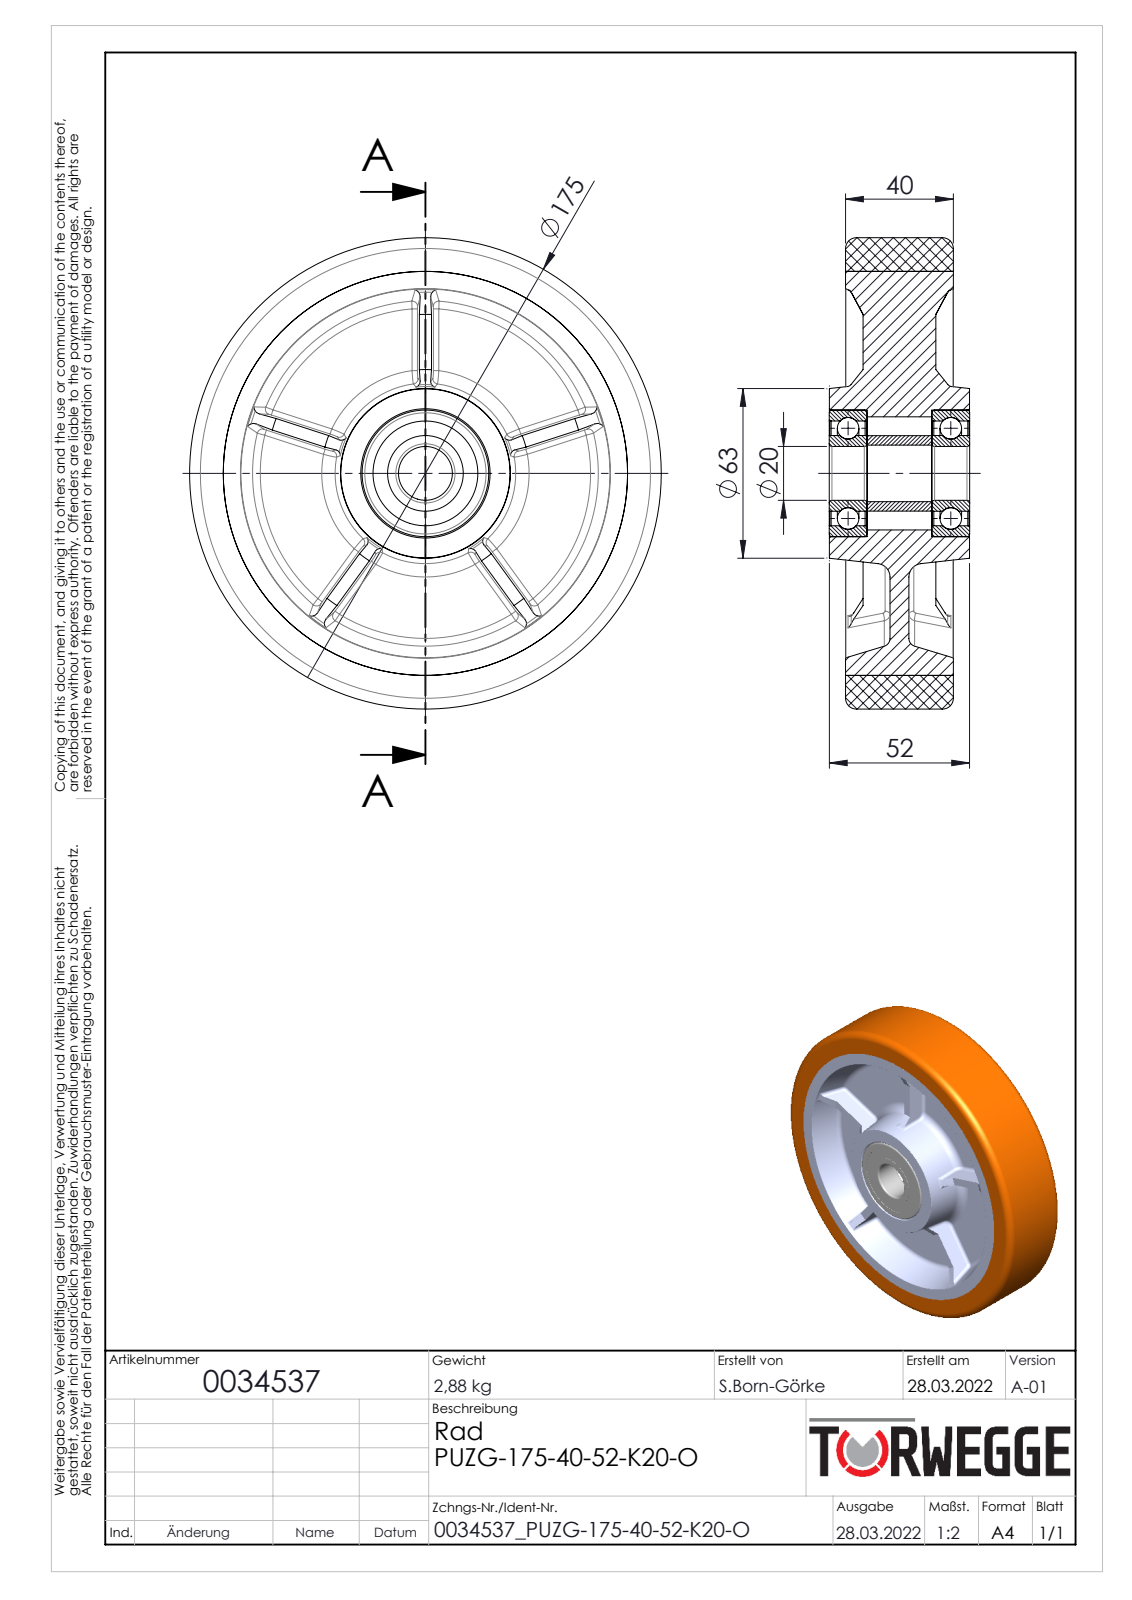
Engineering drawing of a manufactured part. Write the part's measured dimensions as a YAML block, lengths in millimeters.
part_name: "0034537"
step_written_by: "SolidWorks 2020 (AUTOMOTIVE_DESIGN)"
units: millimeters
bodies: {solids: 13, faces: 354, planar: 66, cylindrical: 76, other: 212}
overall_size: [175, 175, 52.1]
volume: 637258
surface_area: 161677
round_holes:
  - {diameter: 20, count: 1}
  - {diameter: 21, count: 1}
  - {diameter: 28.1, count: 1}
  - {diameter: 38.9, count: 1}
  - {diameter: 42, count: 1}
  - {diameter: 47, count: 1}
  - {diameter: 150, count: 1}
round_bosses_or_shafts:
  - {diameter: 175, count: 1}
  - {diameter: 28, count: 1}
partial_cylinders:
  - {radius: 2, count: 20}
face_to_face_distances: [16.5, 23.5, 40, 7, 38.1, 6, 22.5, 29.5, 46, 0.7]
